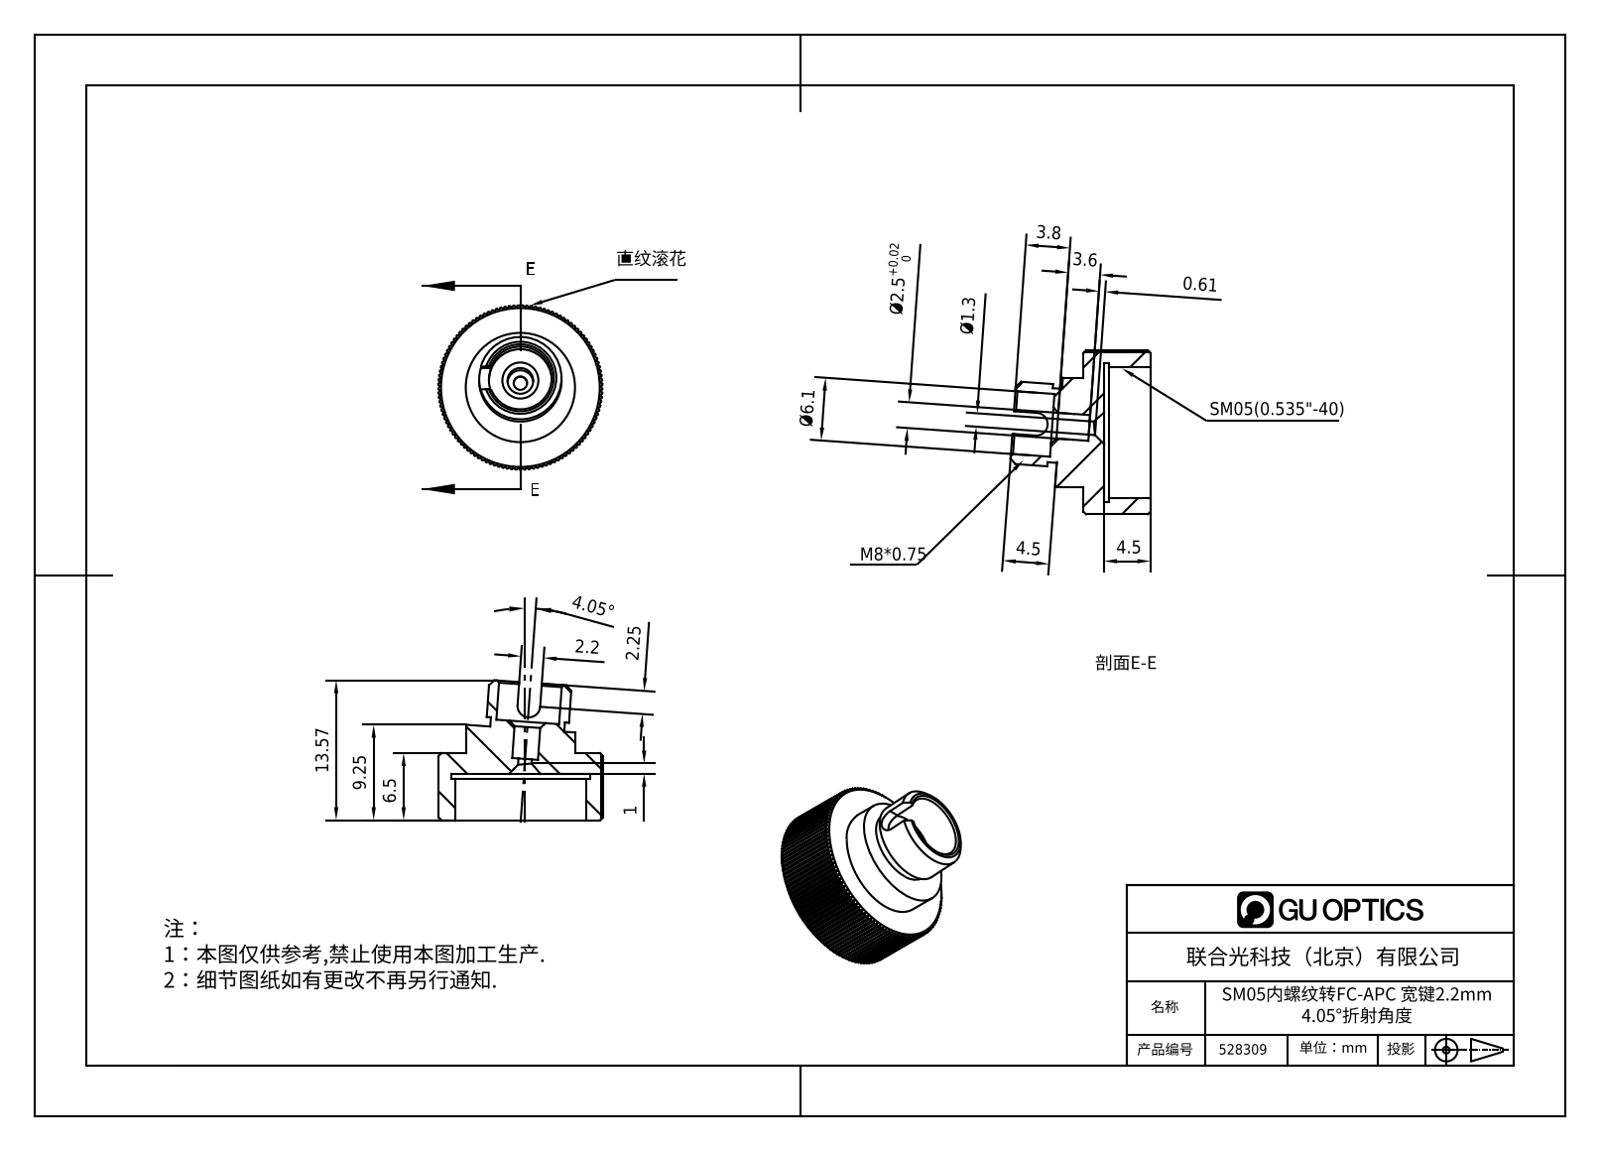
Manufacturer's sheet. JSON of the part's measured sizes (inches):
{"part_name": "528309", "step_written_by": "SolidWorks 2020 (CONFIG_CONTROL_DESIGN)", "units": "inches", "bodies": {"solids": 1, "faces": 394, "planar": 245, "cylindrical": 135, "other": 14}, "overall_size": [0.626, 0.626, 0.534], "volume_in3": 0.06, "surface_area_in2": 2.015, "round_holes": [[0.051, 1], [0.098, 1], [0.24, 1], [0.5, 1], [0.531, 1]], "round_bosses_or_shafts": [[0.417, 1], [0.315, 1], [0.283, 1]], "partial_cylinders_radius": [[0.043, 1], [0.313, 1]], "face_to_face_distances": [0.079, 0.177, 0.256, 0.028, 0.157, 0.02, 0.098, 0.035, 0.142, 0.15]}
